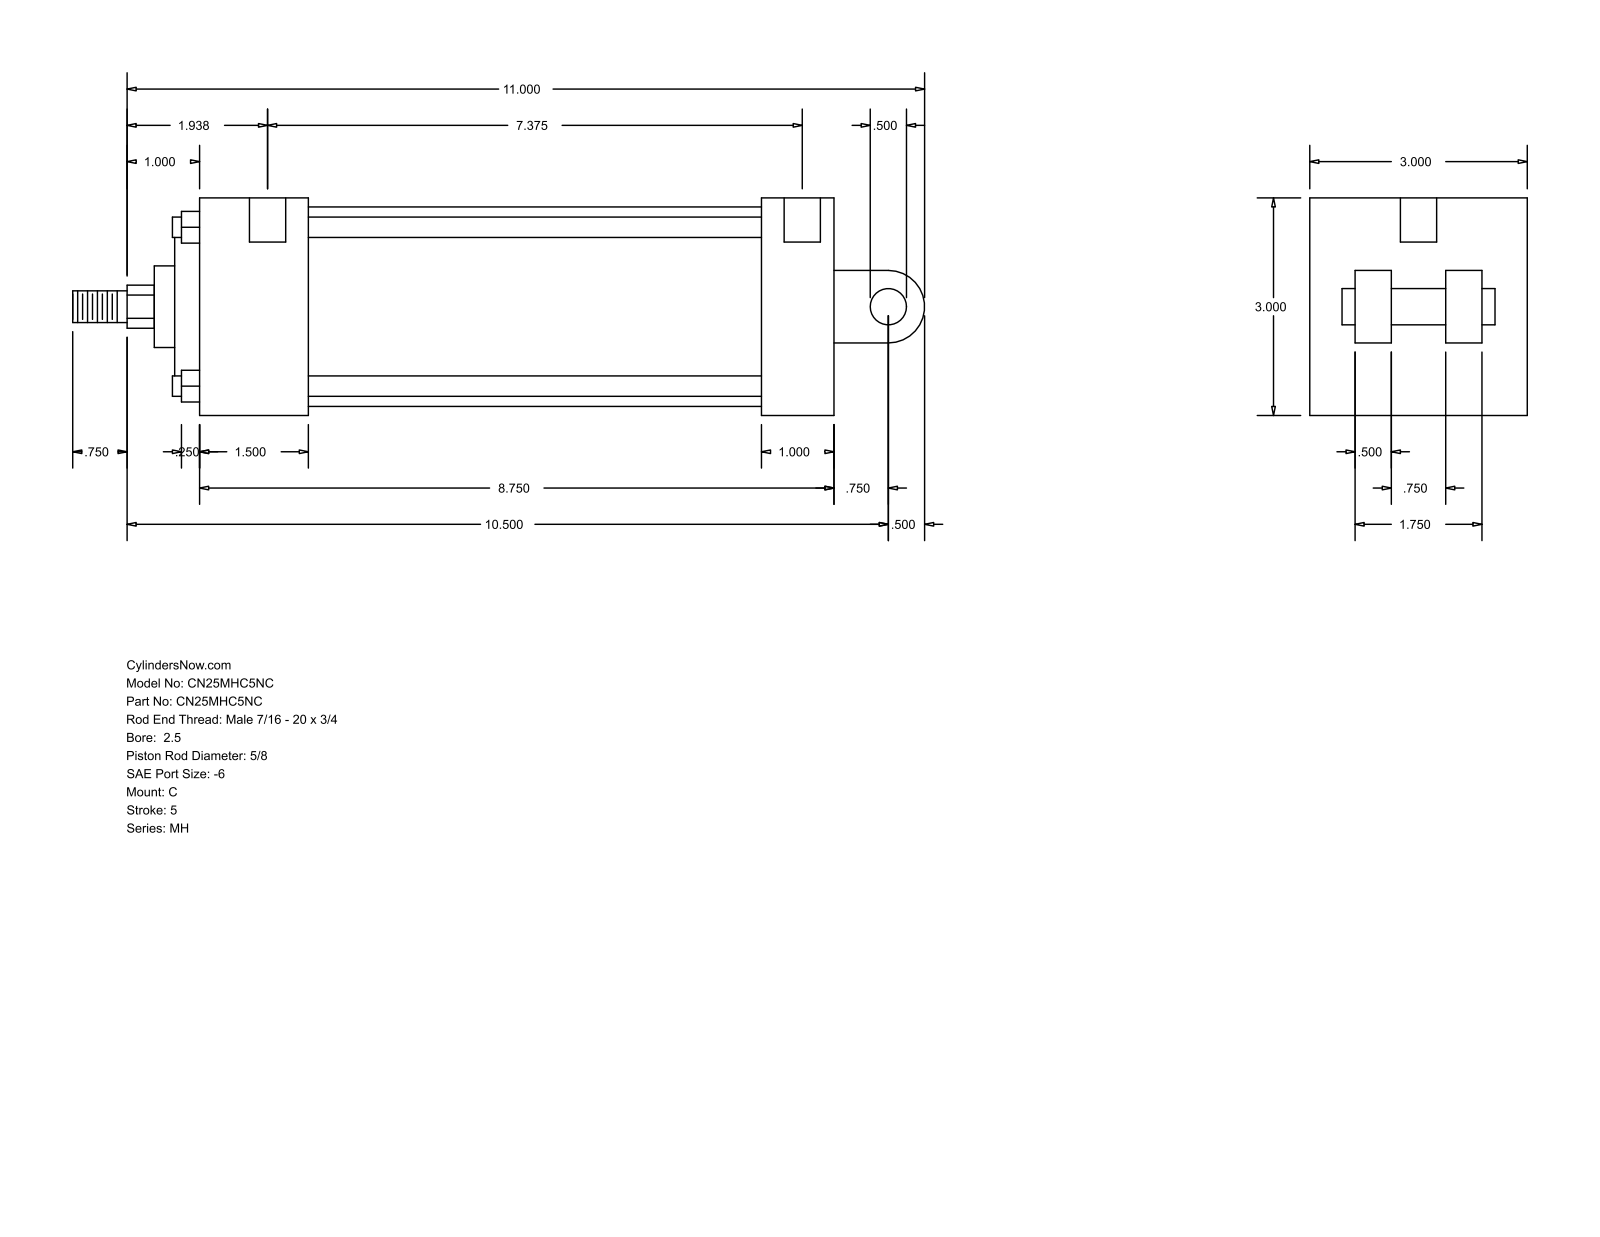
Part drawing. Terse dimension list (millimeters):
name: MH_C__0250_0.625
written by: GSSL Pune (CONFIG_CONTROL_DESIGN)
unit: mm
bodies: 0 solids, 101 faces (71 planar, 30 cylindrical, 0 other)
size: 298.45 × 76.2 × 76.2
holes: 4× ⌀5.56, 2× ⌀12.7
bosses: 4× ⌀7.14, 1× ⌀69.85, 1× ⌀55.55, 1× ⌀28.57, 1× ⌀15.88, 1× ⌀12.7, 1× ⌀11.11
rounds: 1× R7.54, 1× R12.7
face distances: 76.2, 25.4, 222.25, 15.87, 38.1, 196.85, 158.75, 184.15, 8.73, 46.83
hole spacings: 195.26, 3.17, 4.76, 187.33, 190.5, 192.09
